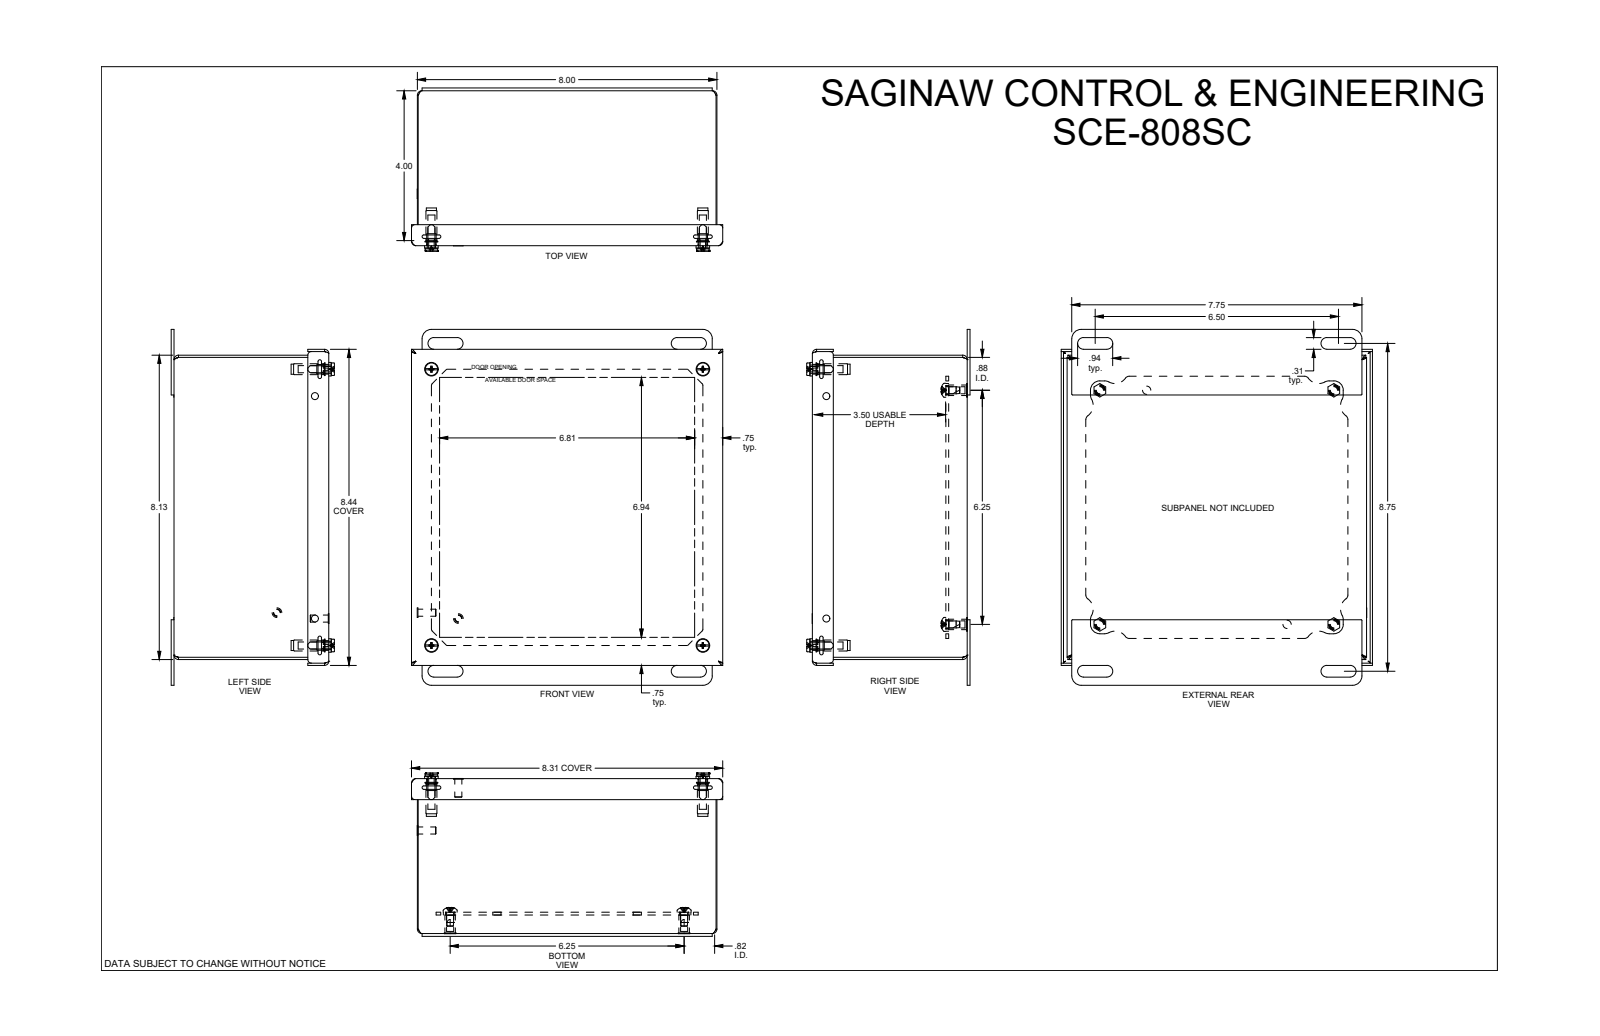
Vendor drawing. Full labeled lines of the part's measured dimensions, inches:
Part name (STEP PRODUCT): SCE-808SC
STEP written by: SolidWorks 2019 (CONFIG_CONTROL_DESIGN)
Units: inches
Bodies: 0 solids, 875 faces (393 planar, 216 cylindrical, 266 other)
Overall size (bounding box): 9.5 × 8.313 × 4.361
Round holes (diameter × count): ⌀0.19 ×8, ⌀0.25 ×8, ⌀0.22 ×4, ⌀0.281 ×4, ⌀0.317 ×4, ⌀0.218 ×2, ⌀0.193 ×1
Round bosses / shafts (diameter × count): ⌀0.188 ×10, ⌀0.373 ×4, ⌀0.362 ×4, ⌀0.34 ×4, ⌀0.334 ×4, ⌀0.292 ×4, ⌀0.28 ×4, ⌀0.27 ×4
Partial cylindrical surfaces — rounded edges, fillets, slot ends (radius × count): R0.125 ×16, R0.25 ×16, R0.005 ×8, R0.007 ×8, R0.052 ×8, R0.112 ×8, R0.156 ×8, R0.255 ×8
Main face-to-face distances: 0.06, 0.06, 4.075, 4.015, 4.135, 4.075, 7.94, 3.58, 0.57, 0.51
Hole centre spacings: 0.753, 6.25, 6.773, 6.831, 9.59, 1.25, 1.838, 5
